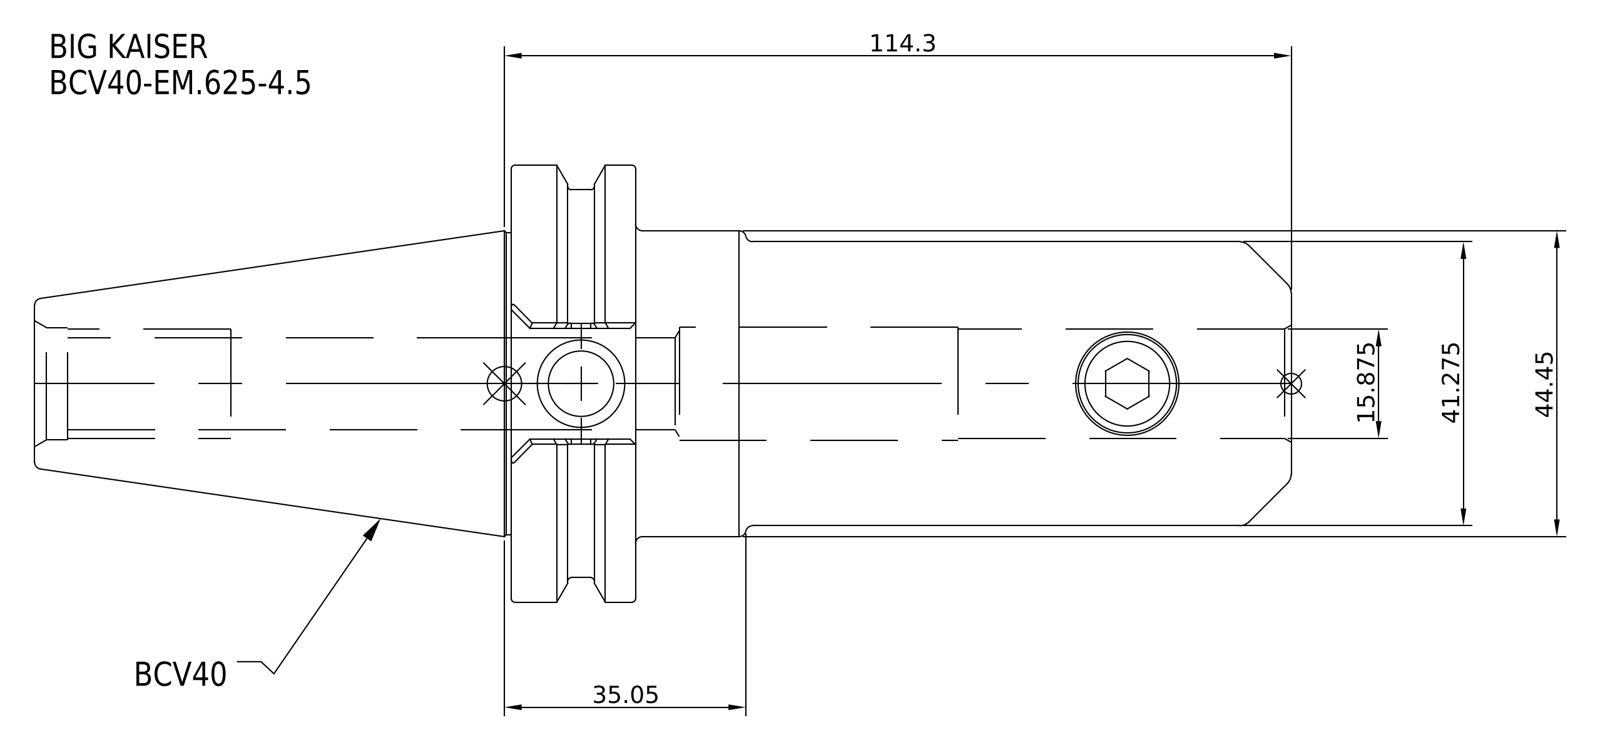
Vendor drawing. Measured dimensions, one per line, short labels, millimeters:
name: BCV40-EM_625-4_5
written by: SolidWorks 2021 (CONFIG_CONTROL_DESIGN)
unit: mm
bodies: 1 solid, 30 faces (8 planar, 14 cylindrical, 8 other)
size: 182.55 × 63.5 × 63.5
volume: 233 404 mm³; area: 33 151 mm²
holes: 1× ⌀15.88
bosses: 1× ⌀63.5, 1× ⌀56.36, 1× ⌀44.45, 1× ⌀41.27
face distances: 18.05, 87.3, 69.25, 95.25, 113.3, 182.55, 79.25, 16, 34.05, 103.3
